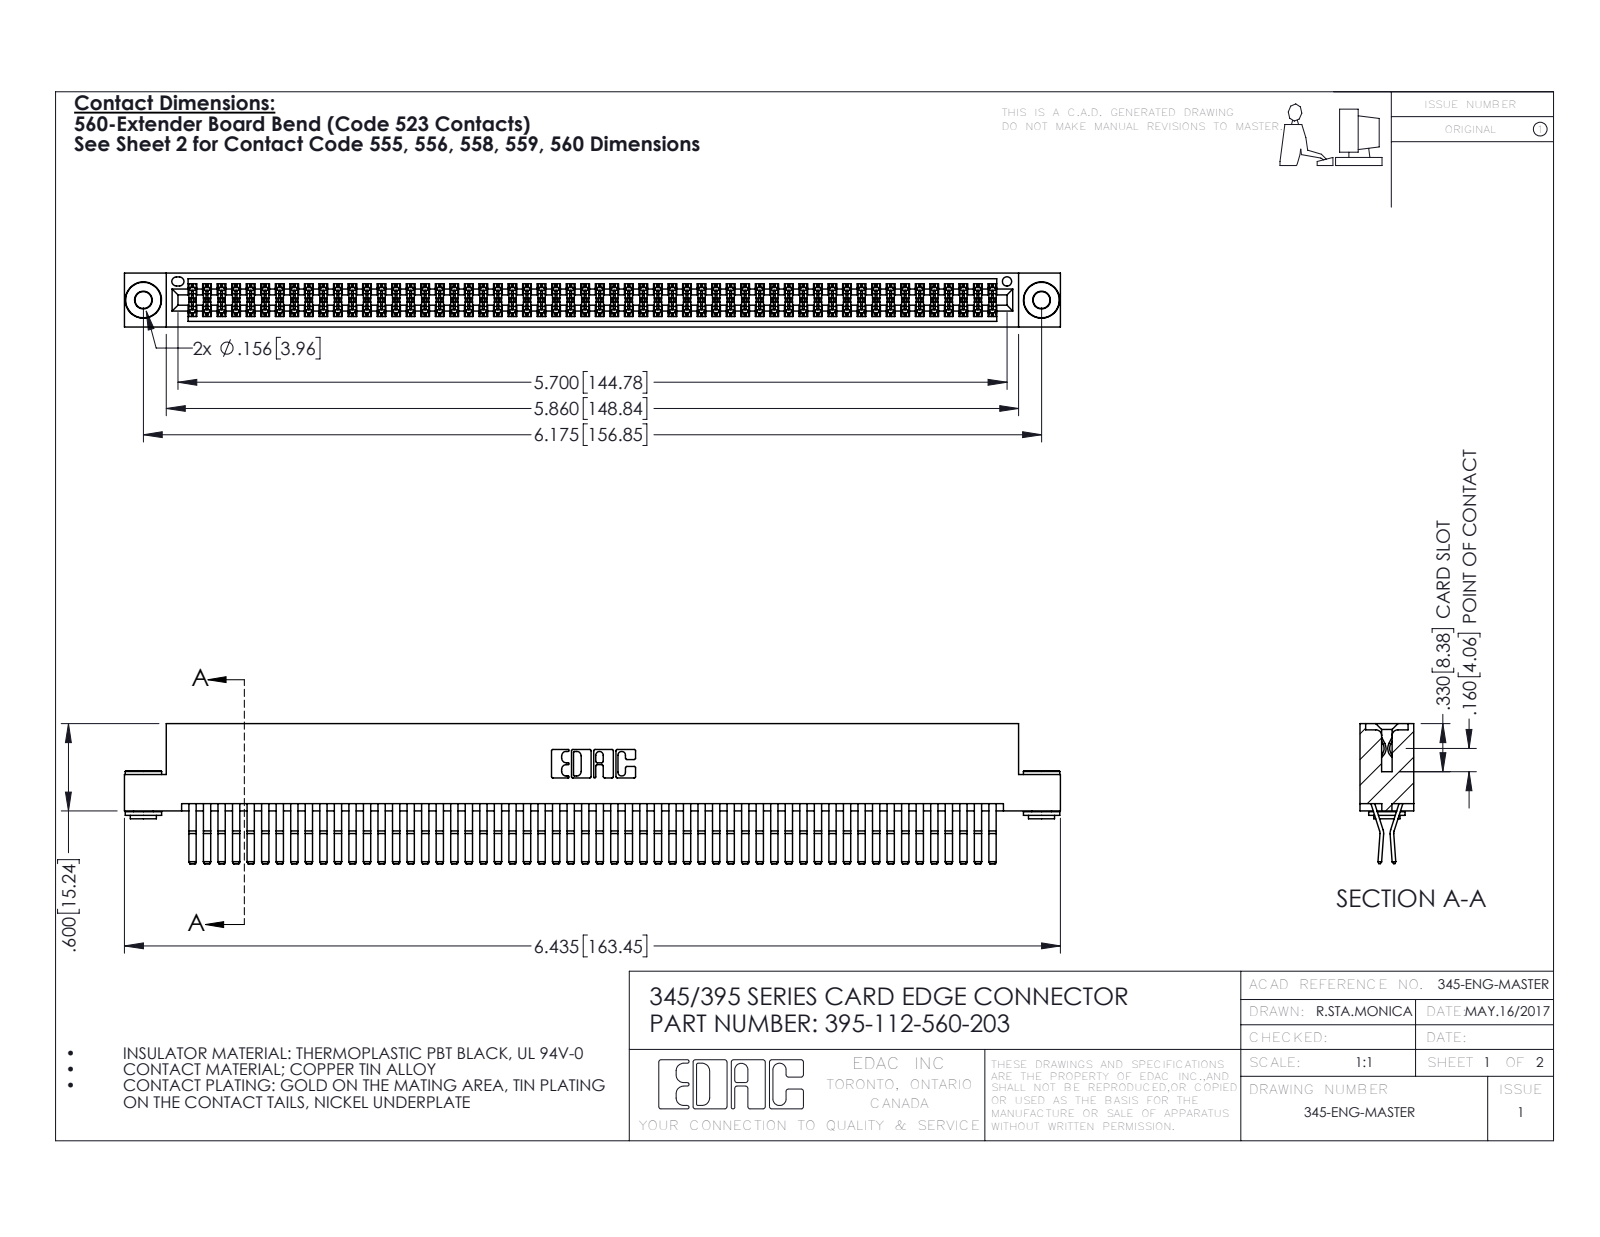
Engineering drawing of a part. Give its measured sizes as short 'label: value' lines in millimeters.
name: 345 Part_Flush Mounting Lugs - 0.156 Dia-TH; 395-112-560-203; 345-250-002_345-250-002-102; 345-292-001_560 Tail
written by: SolidWorks 2016 (CONFIG_CONTROL_DESIGN)
unit: mm
bodies: 115 solids, 5988 faces (3786 planar, 2194 cylindrical, 8 other)
size: 163.4 × 24.4 × 9.4
volume: 16 760 mm³; area: 27 140 mm²
holes: 2× ⌀2.9, 2× ⌀4, 1× ⌀1.6
bosses: 2× ⌀6.4, 2× ⌀4.6, 2× ⌀3.5
rounds: 168× R0.2, 22× R0.3, 6× R0.2, 6× R0.8, 3× R0.7, 2× R0.3, 2× R0.4, 2× R0.5
face distances: 0.6, 1.8, 7.6, 9.4, 5.1, 2.5, 6.9, 5.7, 4.4, 3.8
hole spacings: 6.9, 150.9, 156.8
